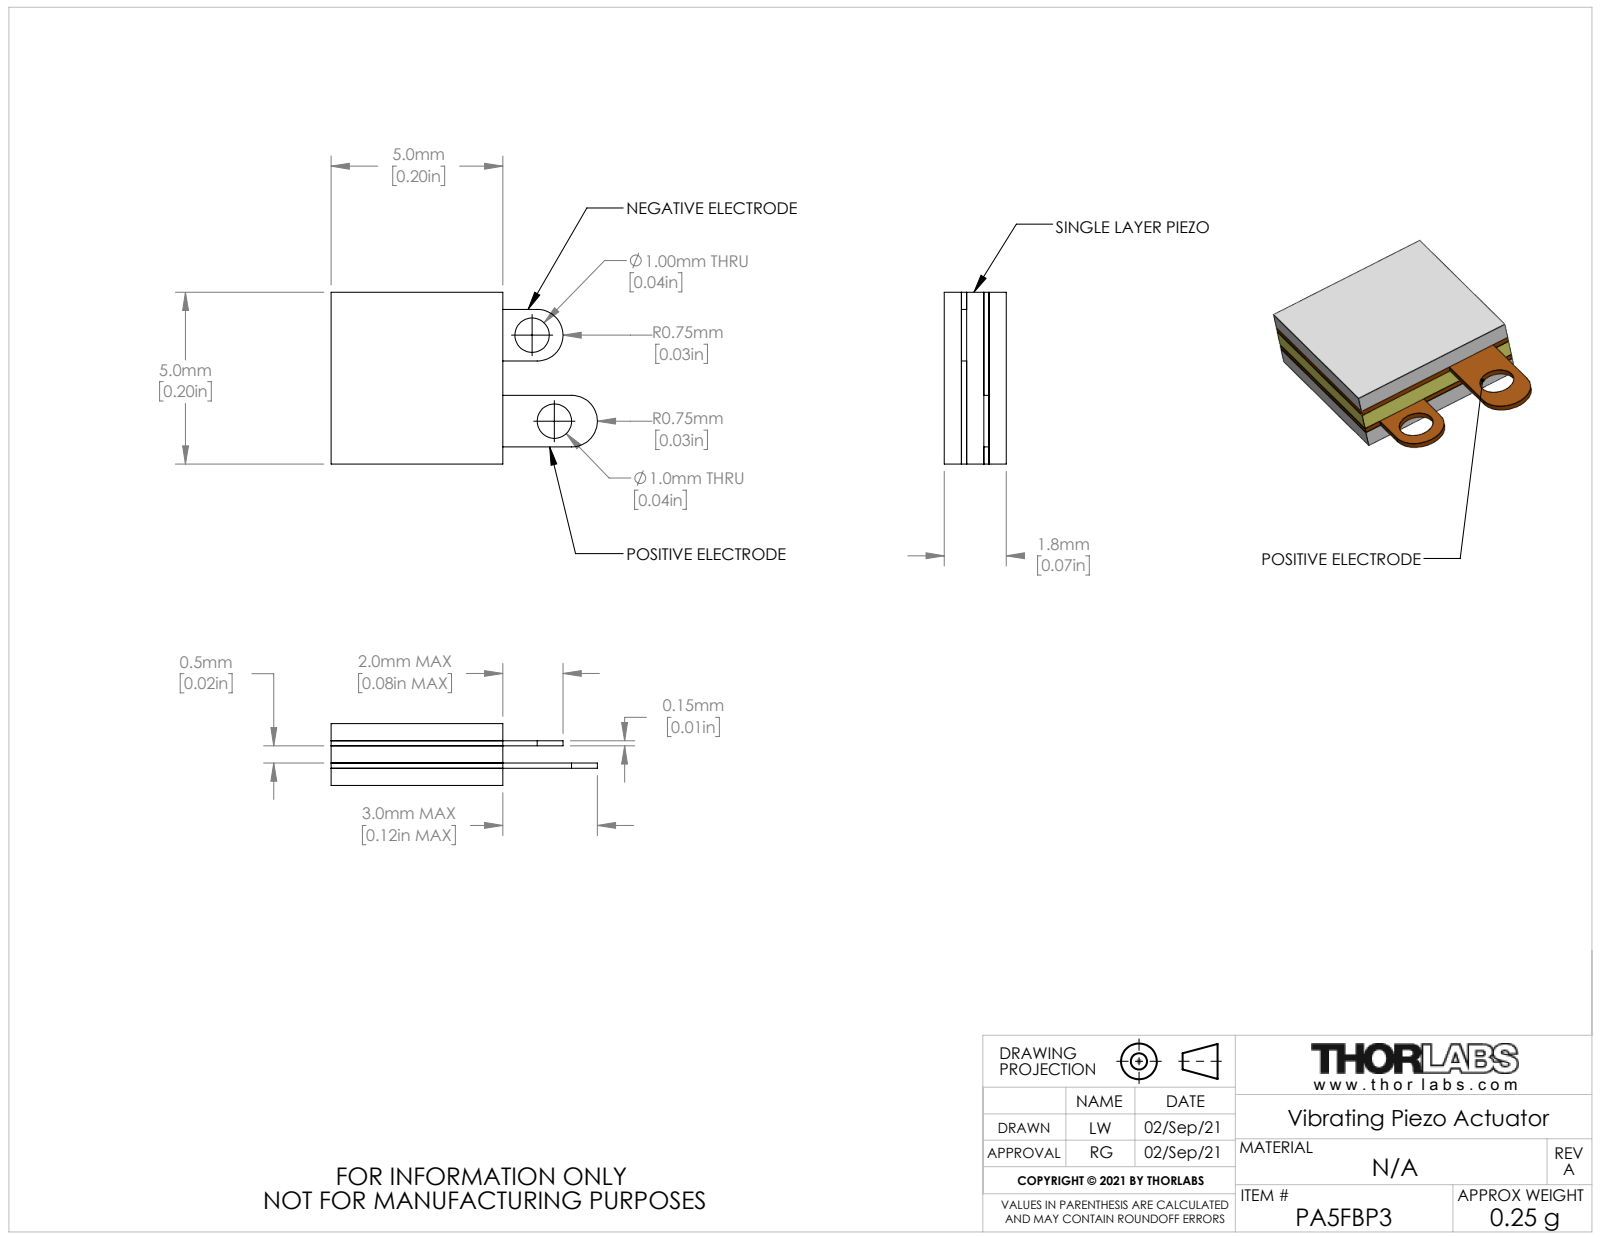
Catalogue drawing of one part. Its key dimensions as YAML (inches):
part_name: "CTN018191-E0W"
step_written_by: "SolidWorks 2018 (AUTOMOTIVE_DESIGN)"
units: inches
bodies: {solids: 5, faces: 42, planar: 36, cylindrical: 6, other: 0}
overall_size: [0.305, 0.197, 0.071]
volume: 0.003
surface_area: 0.46
round_holes:
  - {diameter: 0.039, count: 2}
partial_cylinders:
  - {radius: 0.03, count: 2}
face_to_face_distances: [0.026, 0.02, 0.031, 0.045, 0.051, 0.071, 0.197, 0.079, 0.118, 0.177]
hole_center_spacings: [0.102]
